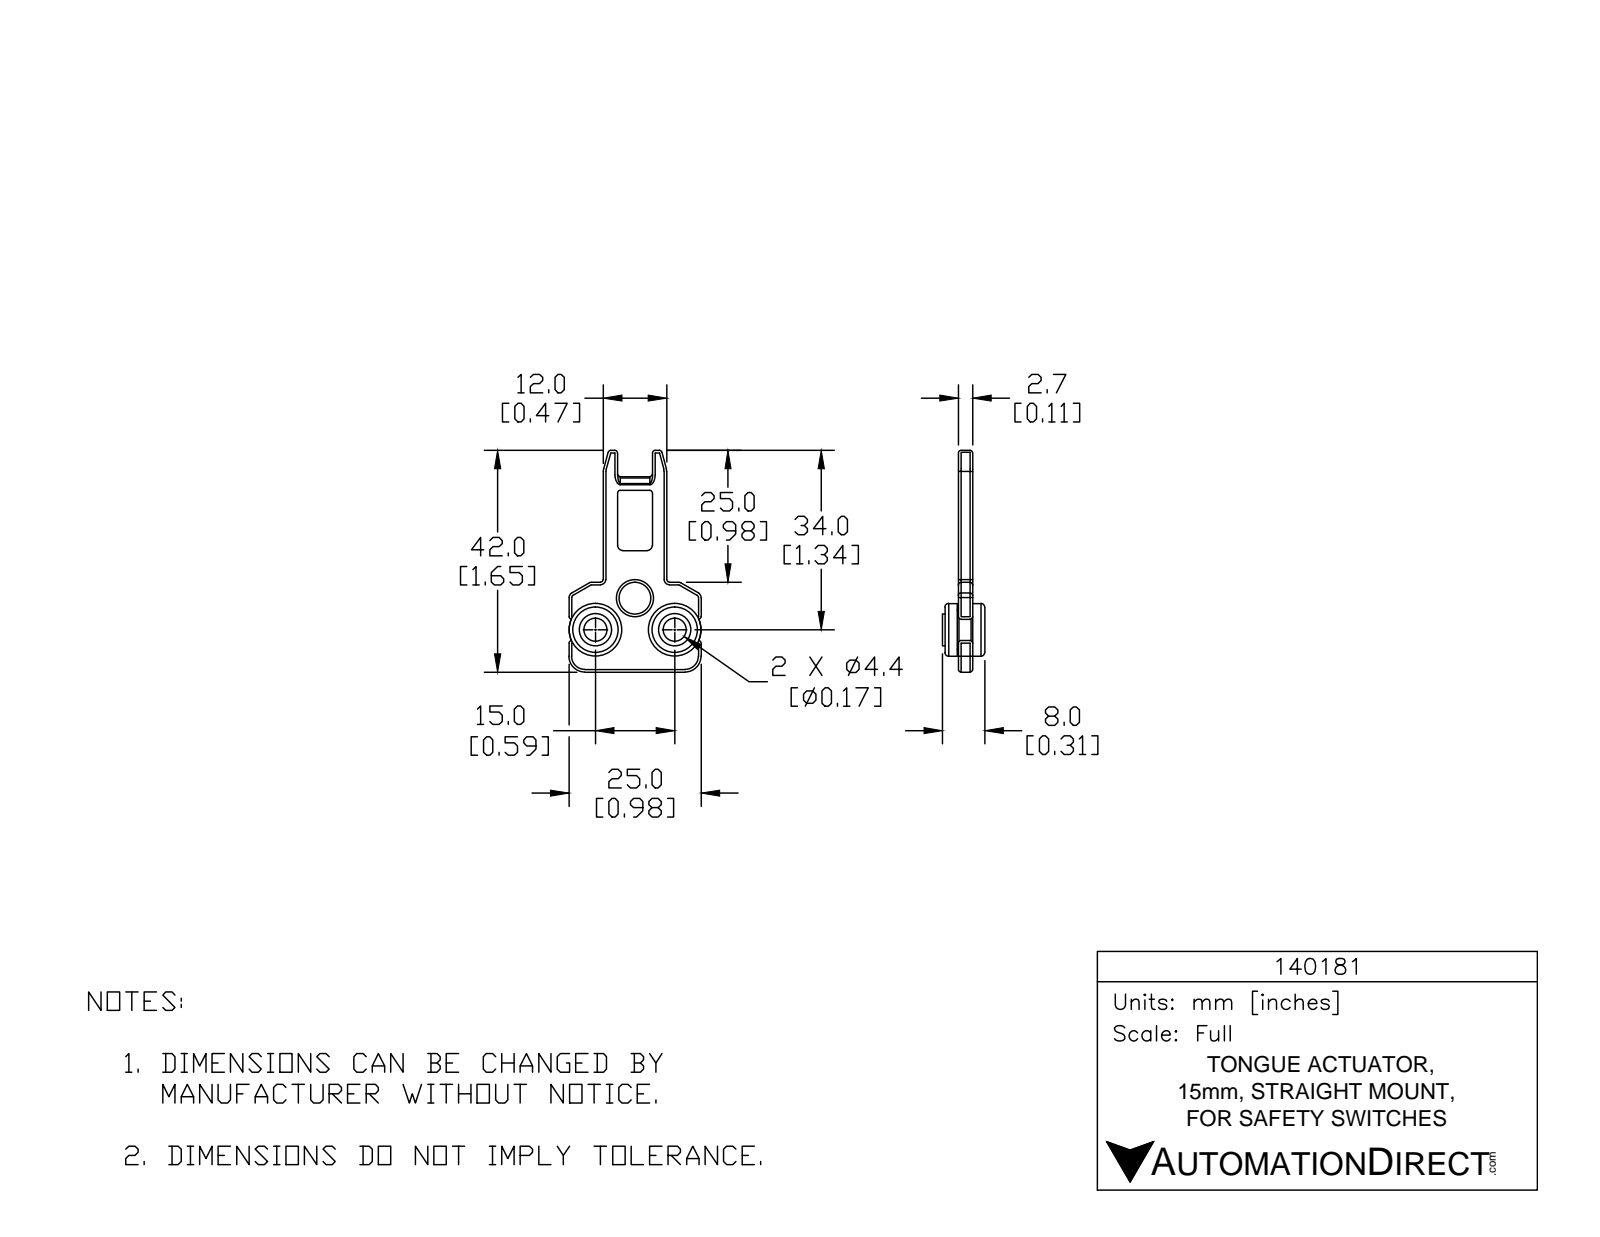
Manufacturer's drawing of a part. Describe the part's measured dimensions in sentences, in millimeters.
The part is named "140181". Its 3-D file was written by "SolidWorks 2014 (AUTOMOTIVE_DESIGN)". It is 5 solids with 264 faces: 42 planar, 118 cylindrical and 104 other. Overall it measures 42 by 25 by 8 millimeters. Its volume is 2 050 cubic millimeters and its surface area 3 036 square millimeters. Round holes: 2 of diameter 4.4, 2 of diameter 5.5, 2 of diameter 7, 1 of diameter 6. Round bosses or shafts: 2 of diameter 10, 2 of diameter 6. Partial cylindrical surfaces (rounded edges, fillets, slot ends): 60 of radius 0.5, 6 of radius 1, 2 of radius 2, 2 of radius 3. The main face-to-face distances are 2.7, 2.3, 5.2, 5, 2.9, 7.5, 2.5, 9.3, 12, 8. The hole center spacings are 9.6, 15.
